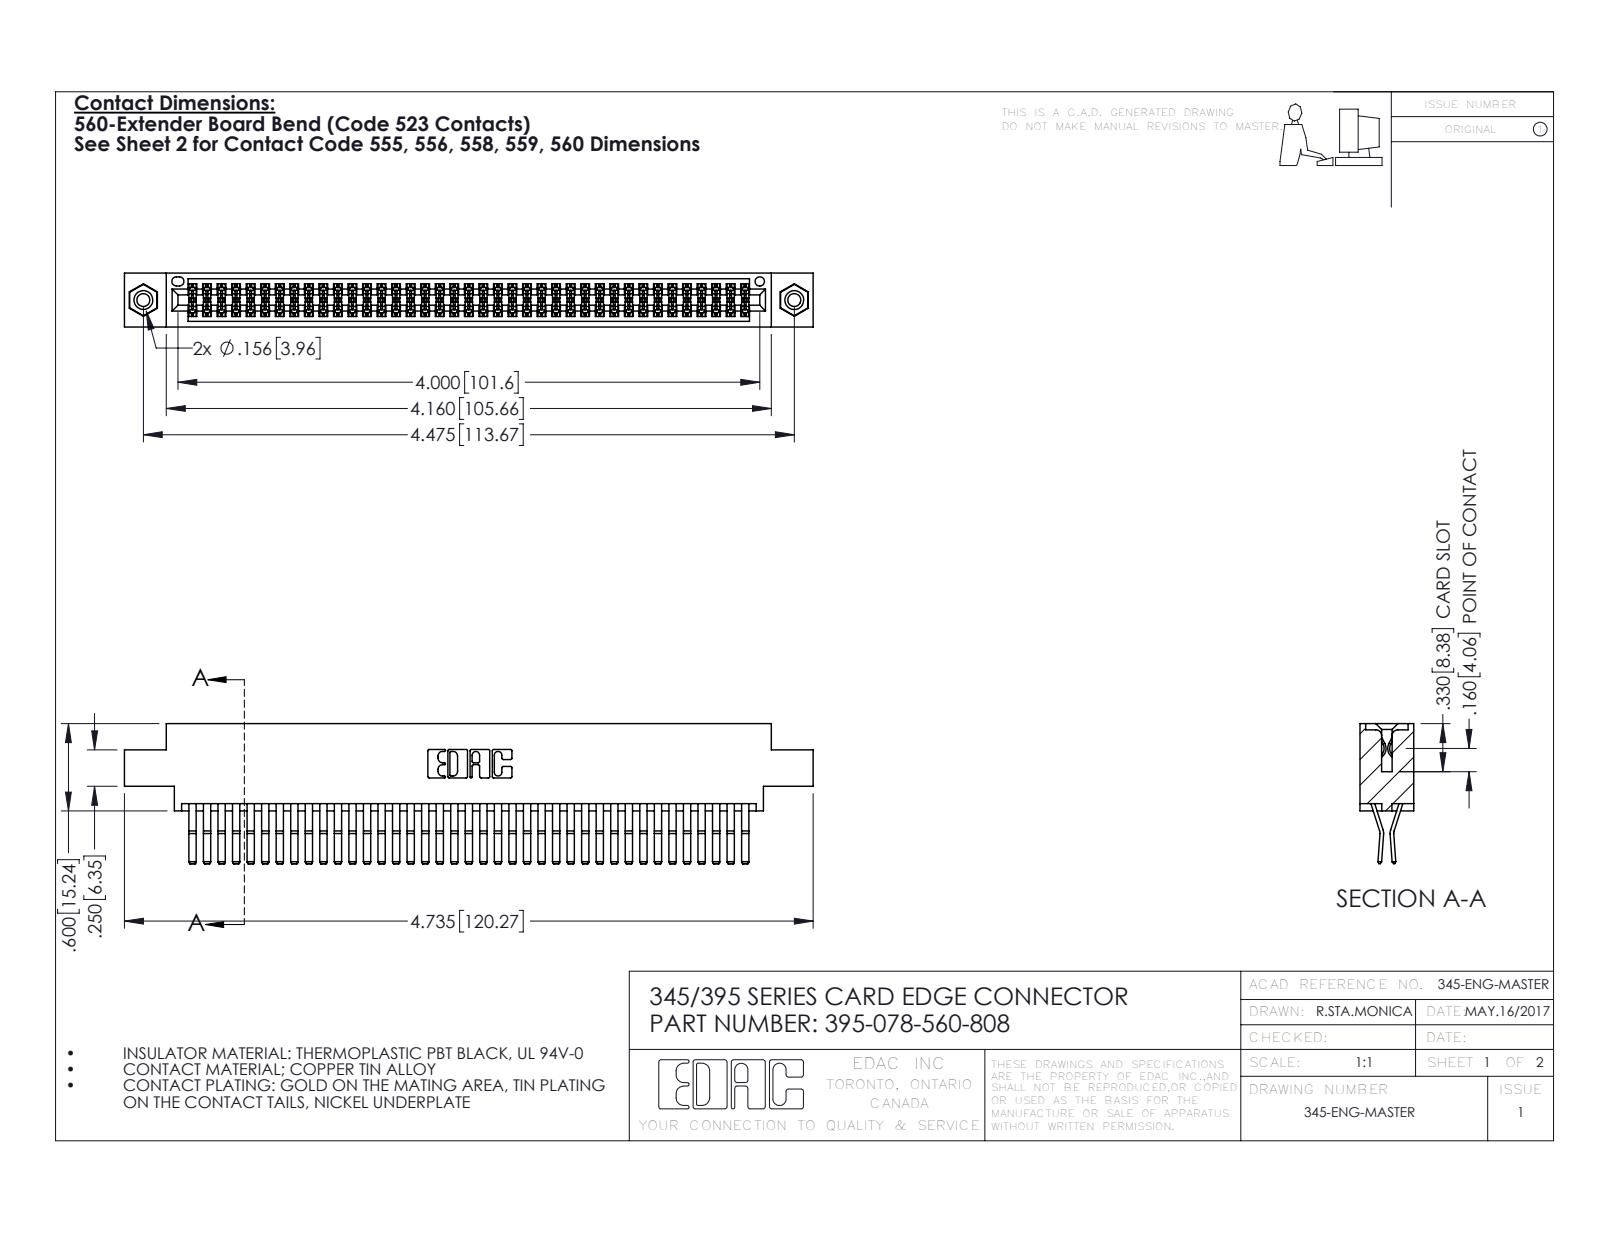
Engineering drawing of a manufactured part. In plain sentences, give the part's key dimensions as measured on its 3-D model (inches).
The part is named "345-292-001_560 Tail; 395-078-560-808; 345 Part_0.170 Offset - 0.156 Dia-TI; 345-250-001_345-250-003-102". Its 3-D file was written by "SolidWorks 2016 (CONFIG_CONTROL_DESIGN)". It is 81 solids with 4246 faces: 2690 planar, 1540 cylindrical and 16 other. Overall it measures 4.735 by 0.962 by 0.37 inches. Its volume is 0.735 cubic inches and its surface area 29.79 square inches. Round holes: 2 of diameter 0.089, 2 of diameter 0.125, 2 of diameter 0.156, 1 of diameter 0.064. Round bosses or shafts: 2 of diameter 0.155. Partial cylindrical surfaces (rounded edges, fillets, slot ends): 117 of radius 0.006, 22 of radius 0.01, 6 of radius 0.007, 6 of radius 0.031, 3 of radius 0.026, 2 of radius 0.01, 2 of radius 0.014, 2 of radius 0.019. The main face-to-face distances are 0.025, 0.072, 0.298, 0.37, 0.2, 0.098, 0.272, 0.225, 0.175, 0.149. The hole center spacings are 0.27, 4.239, 4.475.
